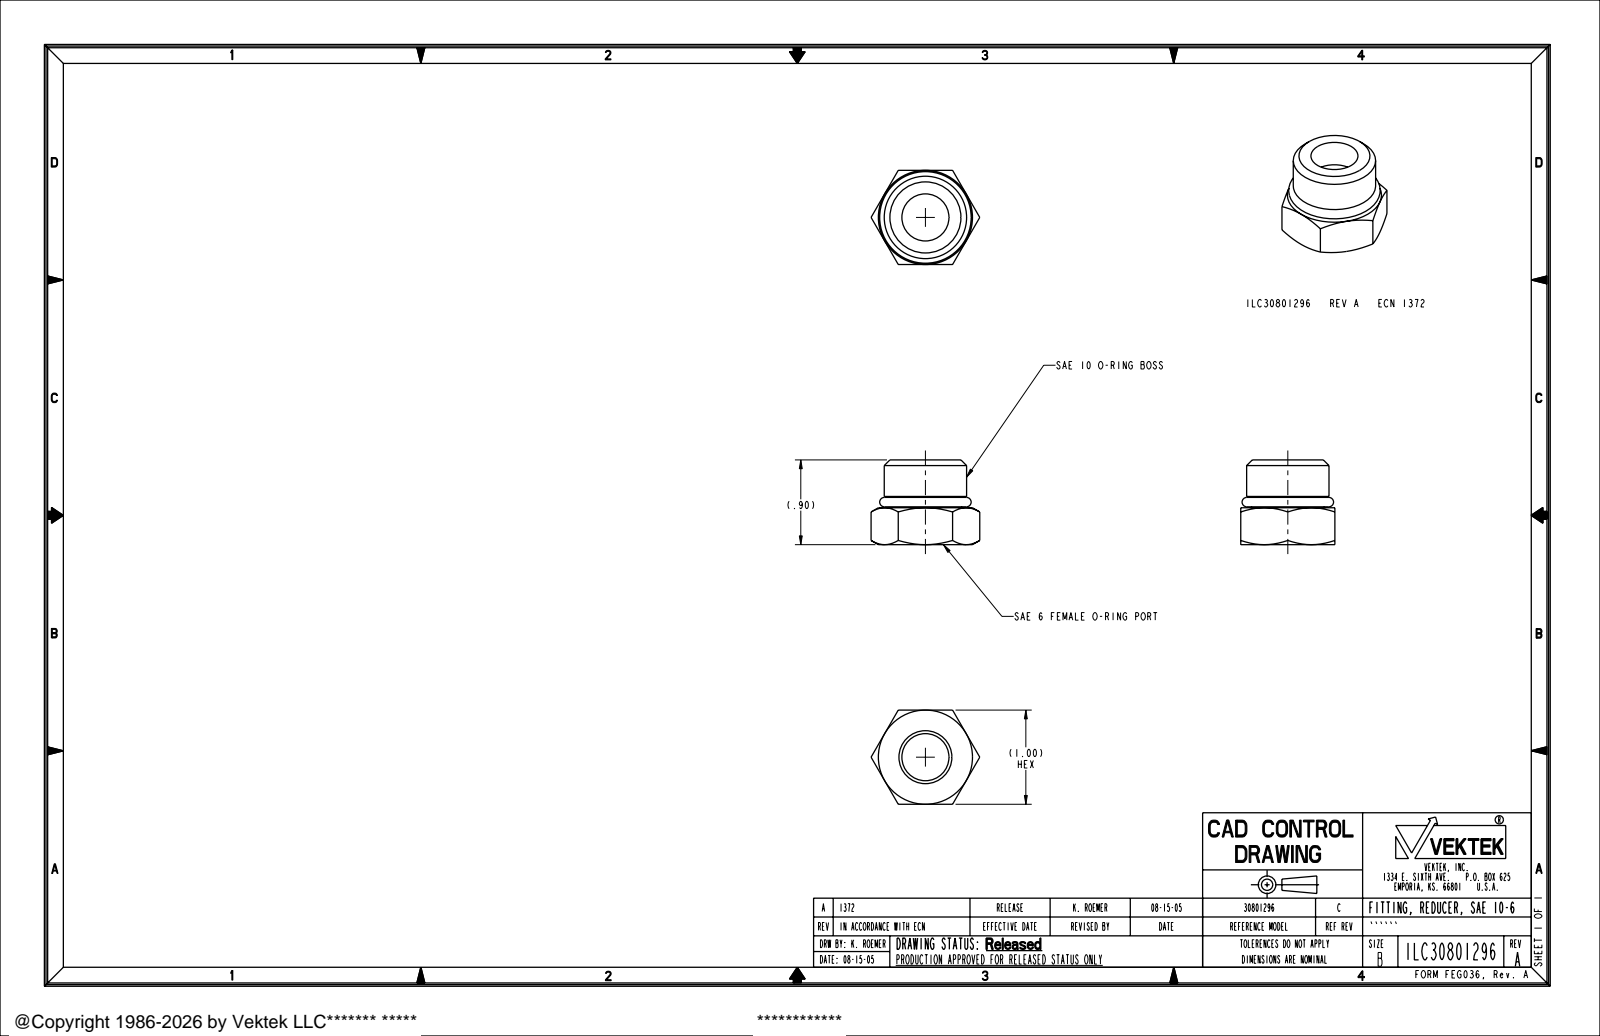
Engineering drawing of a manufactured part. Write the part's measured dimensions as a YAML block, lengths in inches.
part_name: "ILC30801296"
step_written_by: "PRO/ENGINEER BY PARAMETRIC TECHNOLOGY CORPORATION, 2004290 (AUTOMOTIVE_DESIGN_CC2)"
units: inches
bodies: {solids: 2, faces: 37, planar: 11, cylindrical: 8, other: 18}
overall_size: [1.155, 1, 0.9]
volume: 0.435
surface_area: 6.537
round_holes:
  - {diameter: 0.5, count: 1}
  - {diameter: 0.563, count: 1}
round_bosses_or_shafts:
  - {diameter: 0.875, count: 1}
  - {diameter: 0.77, count: 1}
face_to_face_distances: [1, 0.392, 0.9, 0.508, 0.512, 0.12, 0.388, 0.609, 0.217, 0.097]
